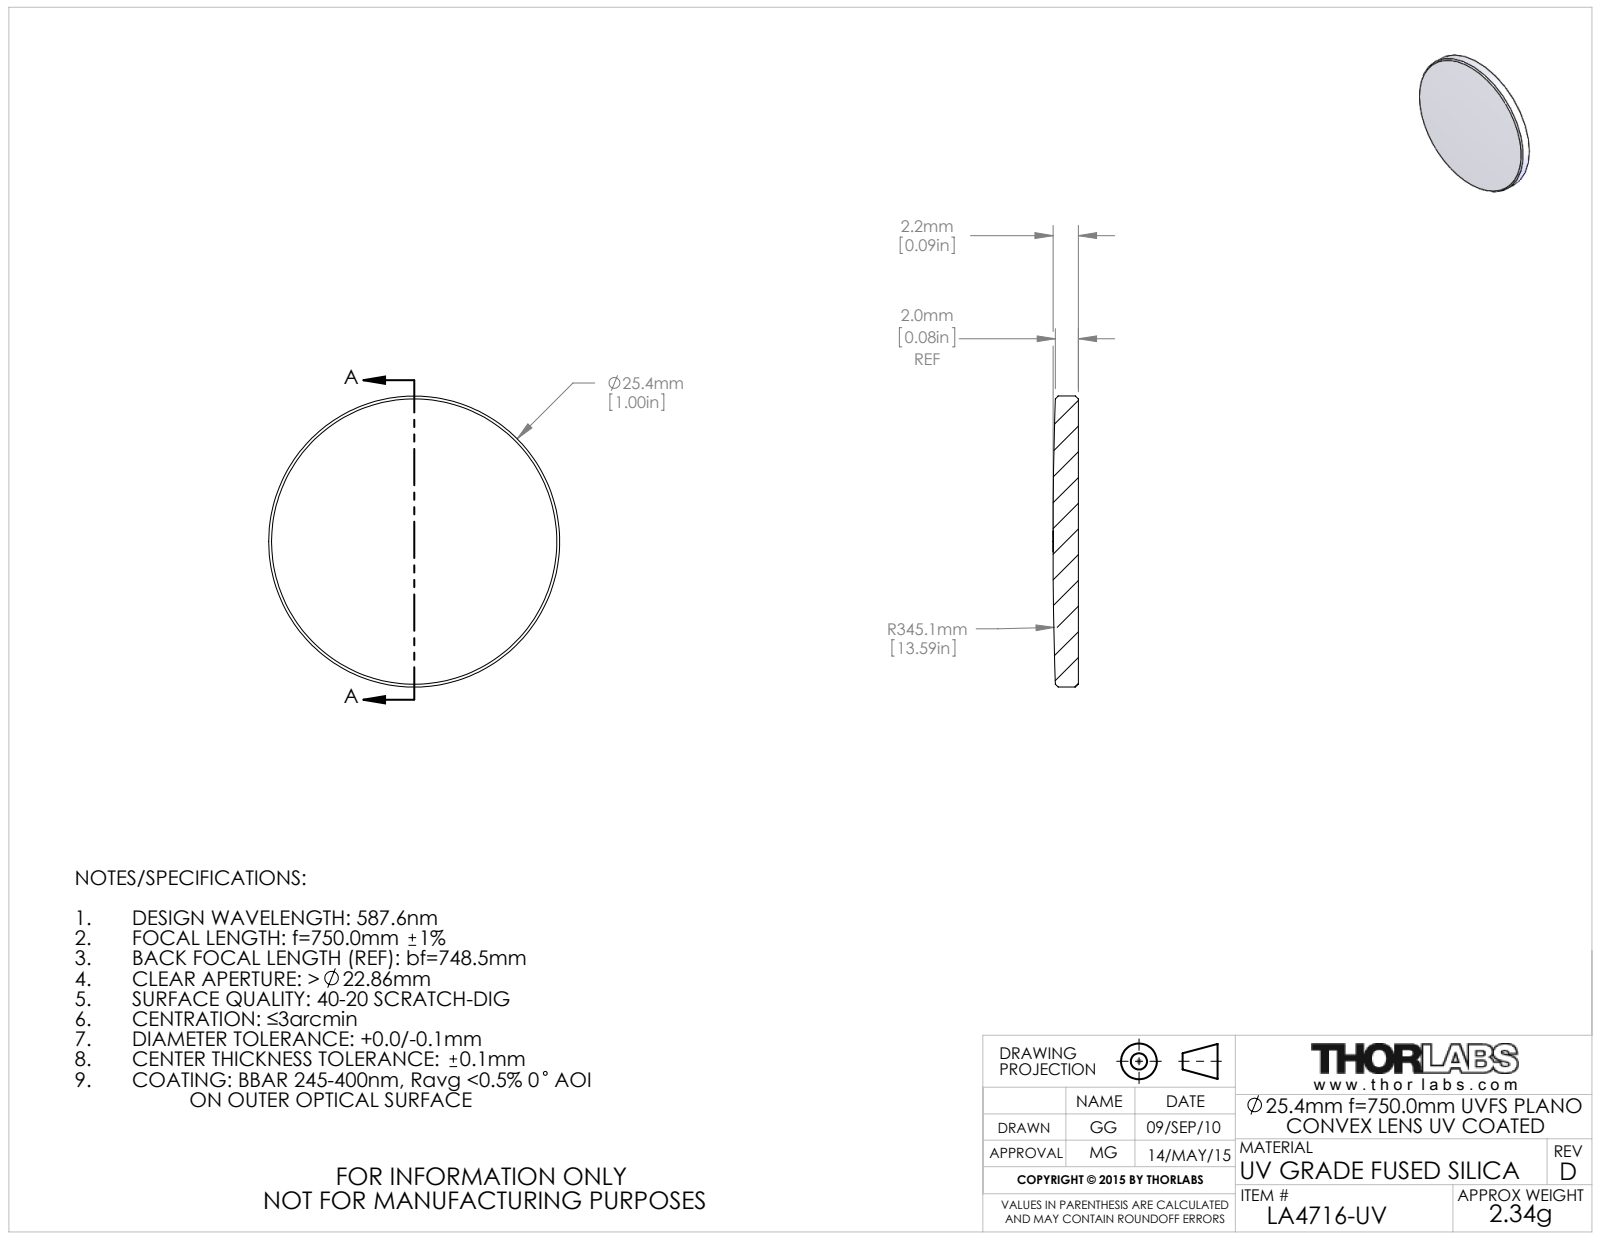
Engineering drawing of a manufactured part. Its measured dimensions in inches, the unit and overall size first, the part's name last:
Units: inches
Overall size (bounding box): 1 × 1 × 0.087
Round bosses / shafts (diameter × count): ⌀1 ×1
Volume: 0.065 in³ · Surface area: 1.783 in²
Bodies: 1 solid, 9 faces (1 planar, 2 cylindrical, 6 other)
Part name (STEP PRODUCT): 4290-E0W
STEP written by: SolidWorks 2014 (CONFIG_CONTROL_DESIGN)
